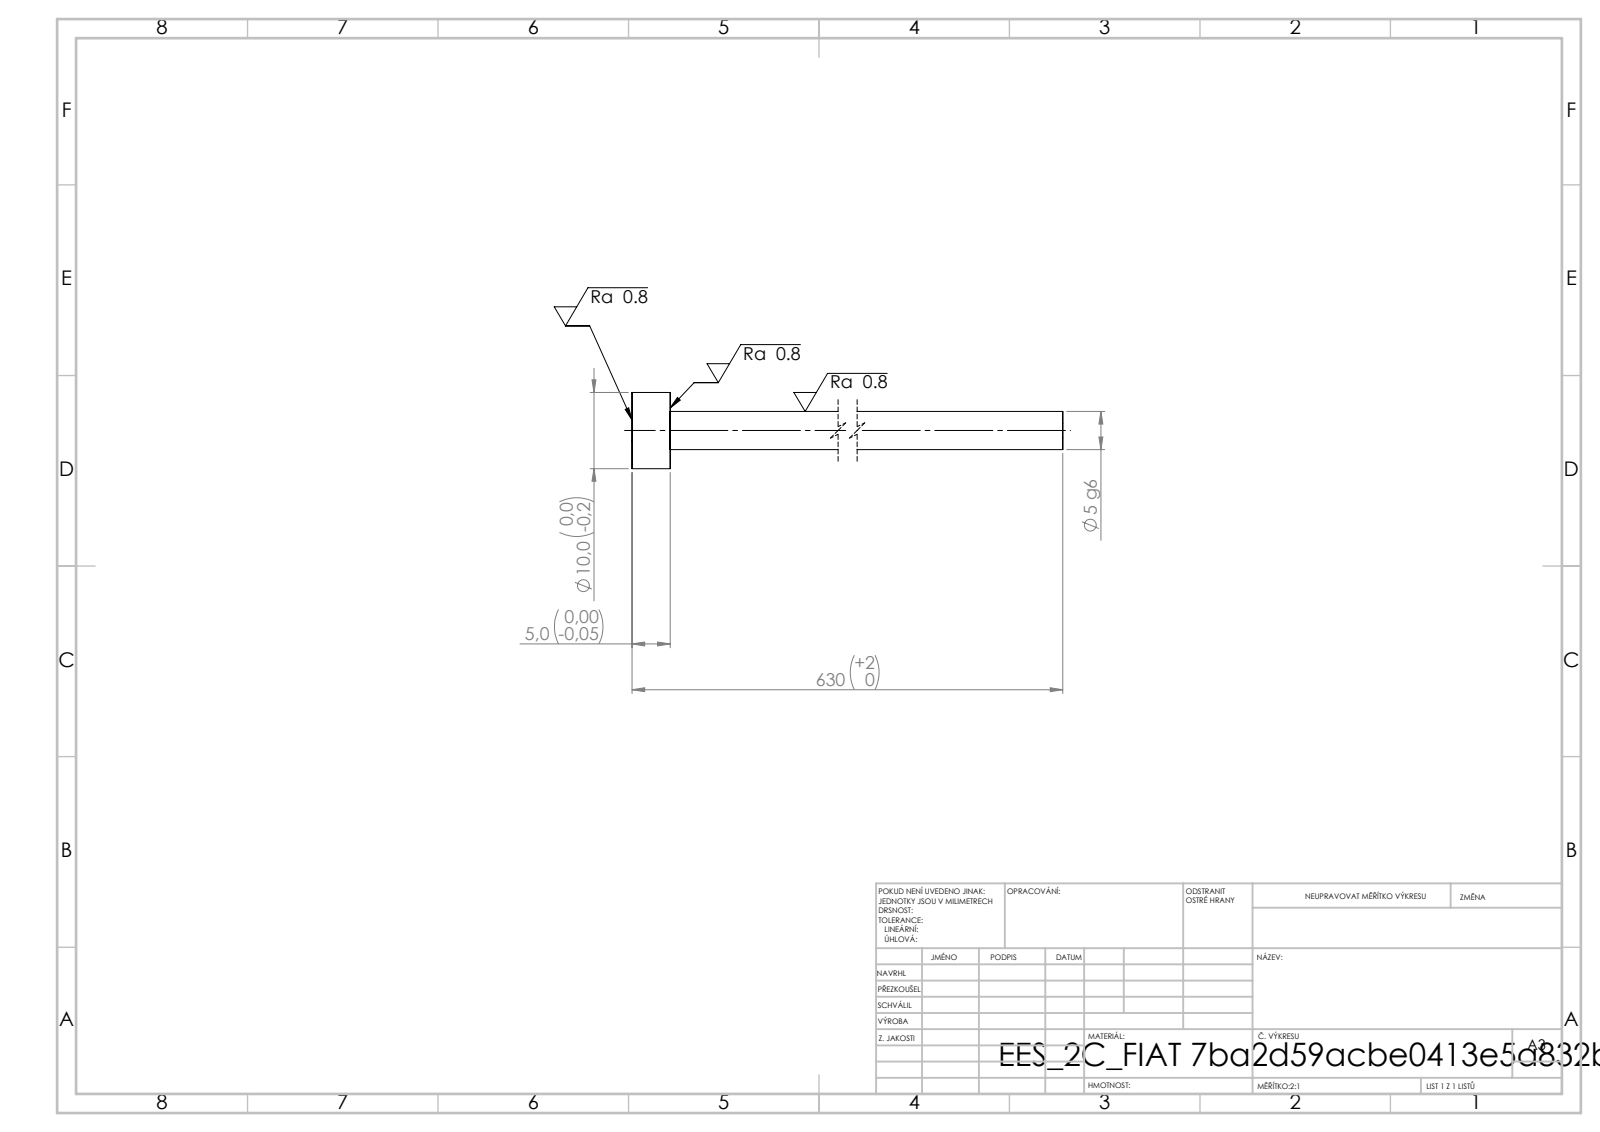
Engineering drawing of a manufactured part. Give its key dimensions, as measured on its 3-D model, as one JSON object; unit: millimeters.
{"step_written_by": "SolidWorks 2019 (CONFIG_CONTROL_DESIGN)", "units": "millimeters", "bodies": {"solids": 1, "faces": 7, "planar": 3, "cylindrical": 4, "other": 0}, "overall_size": [630, 10, 10], "volume_mm3": 12665, "surface_area_mm2": 10132, "round_bosses_or_shafts": [[10, 1], [5, 1]], "face_to_face_distances": [5, 630, 625]}
